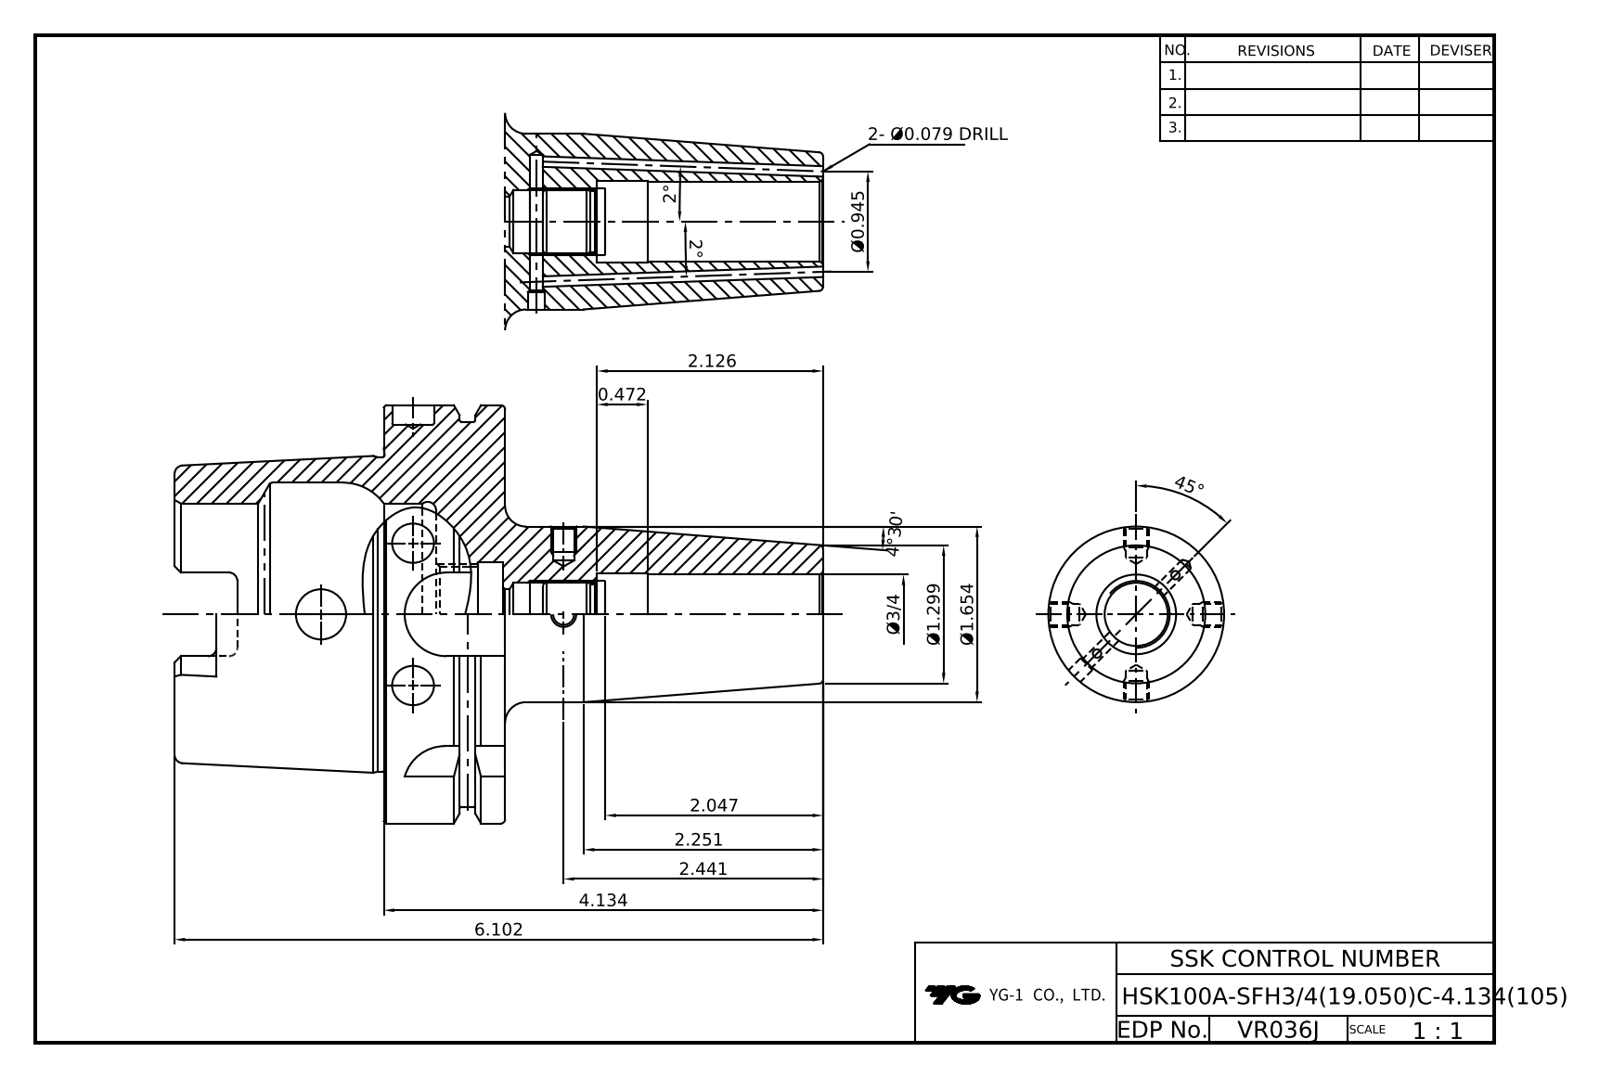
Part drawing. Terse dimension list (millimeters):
name: LO-HSK100A-SFH19.05C-105
written by: Autodesk Inventor 2022 (AUTOMOTIVE_DESIGN)
unit: mm
bodies: 1 solid, 119 faces (38 planar, 37 cylindrical, 44 other)
size: 155 × 100 × 100
volume: 324 295 mm³; area: 63 026 mm²
holes: 2× ⌀2.5, 2× ⌀12, 1× ⌀10, 1× ⌀14.92, 1× ⌀19.05, 1× ⌀20.25, 1× ⌀22.38, 1× ⌀25, 1× ⌀53, 1× ⌀63
bosses: 1× ⌀100, 1× ⌀92, 1× ⌀75.41, 1× ⌀42
rounds: 6× R2, 4× R4.88, 4× R10
face distances: 29, 12.5, 16.5, 62.5, 50, 79, 28.5, 155, 105, 92.5
